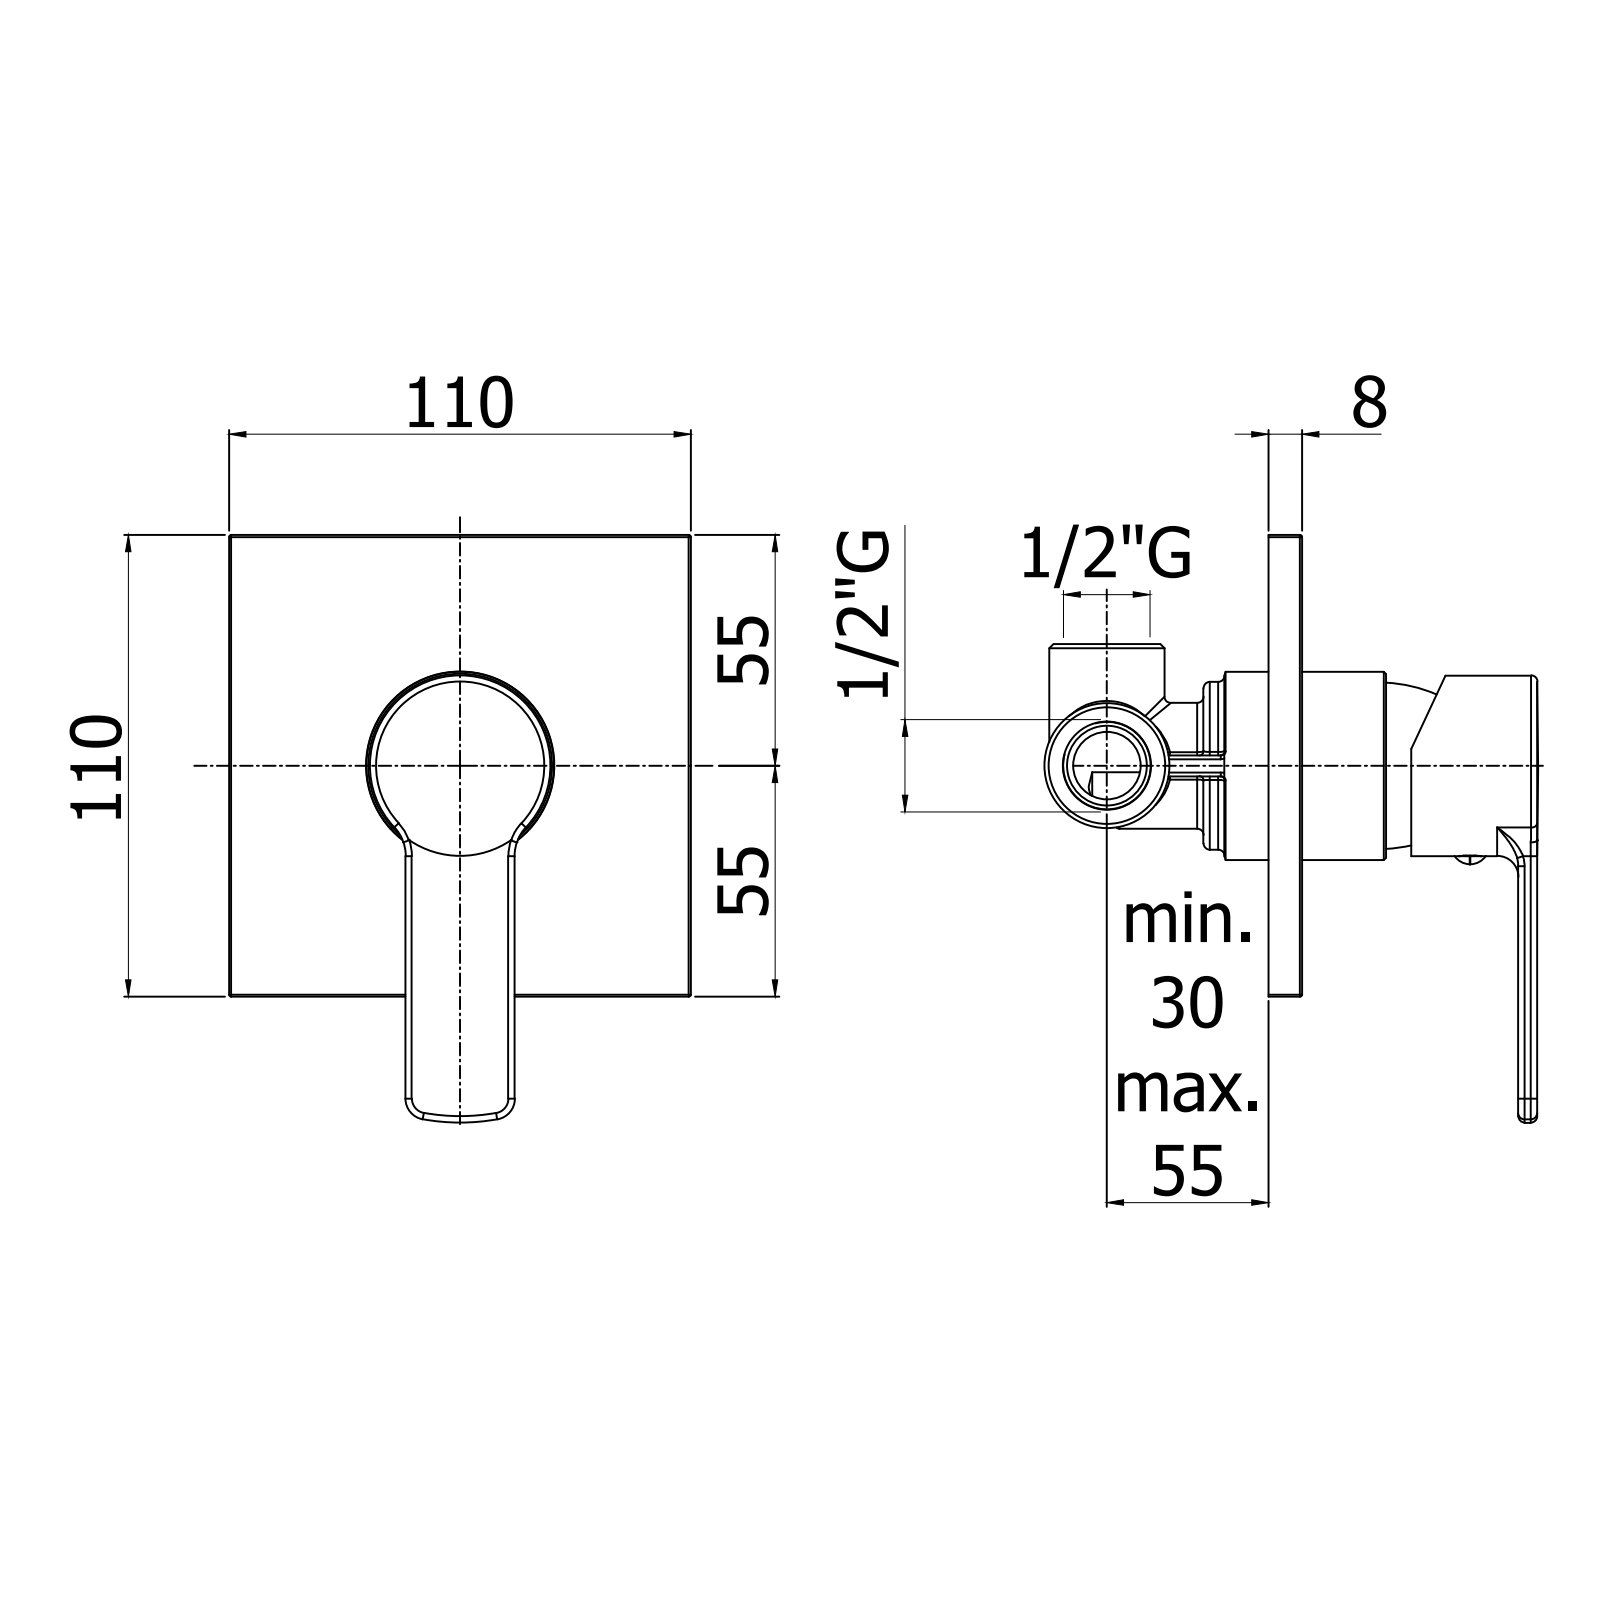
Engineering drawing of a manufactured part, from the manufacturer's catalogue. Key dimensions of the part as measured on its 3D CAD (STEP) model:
Part name (STEP PRODUCT): RED010CR
STEP written by: CREO PARAMETRIC BY PTC INC, 2020044 (CONFIG_CONTROL_DESIGN)
Units: millimetres
Bodies: 2 solids, 1112 faces (611 planar, 289 cylindrical, 212 other)
Overall size (bounding box): 140 × 110 × 64.83
Volume: 115 331 mm³ · Surface area: 72 941 mm²
Round holes (diameter × count): ⌀3.3 ×2, ⌀4 ×2, ⌀3 ×1, ⌀4.5 ×1, ⌀5 ×1, ⌀19.5 ×1, ⌀19.9 ×1, ⌀26.8 ×1, ⌀29 ×1, ⌀31 ×1, ⌀32.4 ×1, ⌀36 ×1
Round bosses / shafts (diameter × count): ⌀51 ×1, ⌀44.8 ×1, ⌀43 ×1, ⌀35 ×1, ⌀32.2 ×1, ⌀23.5 ×1, ⌀23.4 ×1, ⌀21.8 ×1
Partial cylindrical surfaces — rounded edges, fillets, slot ends (radius × count): R0.5 ×82, R0.15 ×11, R1 ×6, R0.3 ×4, R1.5 ×4, R2 ×4, R5 ×2, R10 ×2
Main face-to-face distances: 7, 2, 1, 8, 6, 2.5, 5, 0.5, 108, 59.1
Hole centre spacings: 12.5
